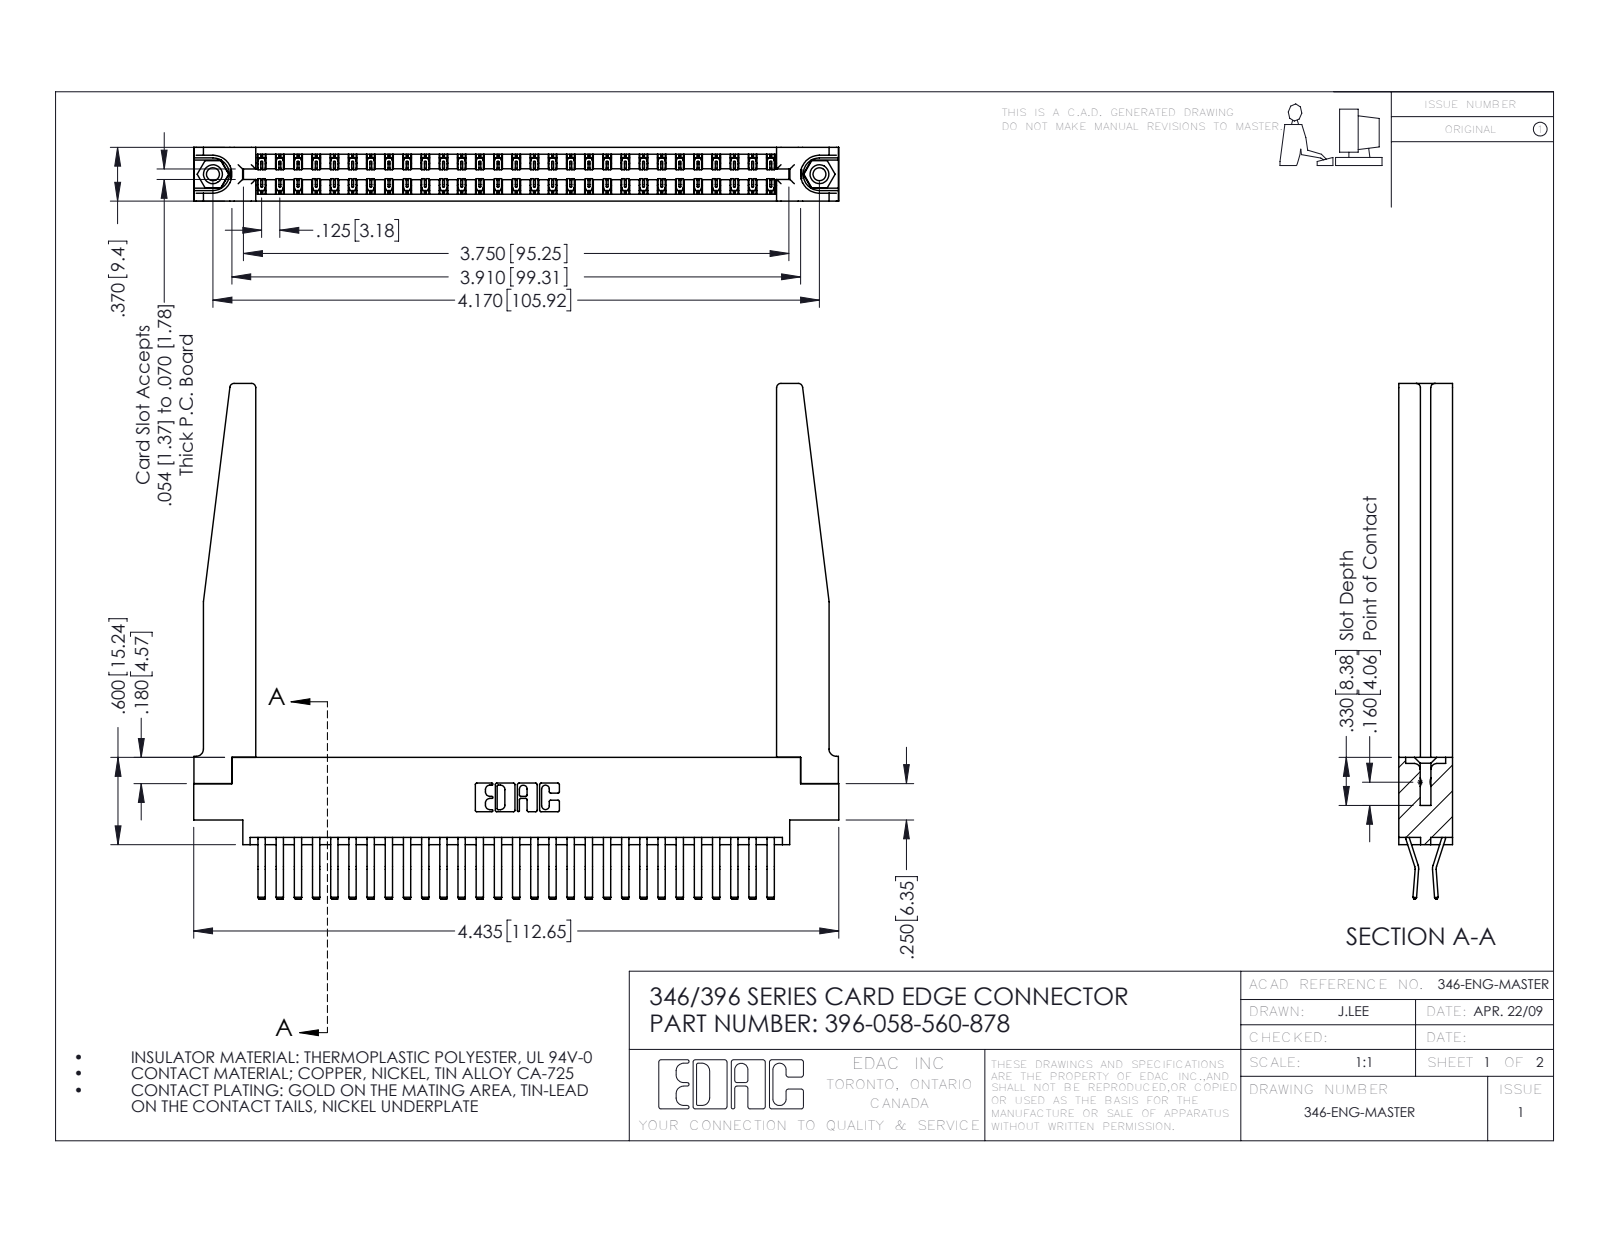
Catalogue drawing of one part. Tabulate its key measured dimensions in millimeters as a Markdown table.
| quantity | value |
| --- | --- |
| part name | 396-058-560-878; 345-292-001_560 Tail; 345-250-001_345-250-001-102; 346 Part_0.170 Offset - 0.156 Dia-TH (+1 more) |
| STEP written by | SolidWorks 2016 (CONFIG_CONTROL_DESIGN) |
| units | millimeters |
| bodies | 63 solids, 3492 faces (2252 planar, 1188 cylindrical, 52 other) |
| overall size | 112.6 × 90 × 9.4 |
| volume | 18 030 mm³ |
| surface area | 22 800 mm² |
| round holes (diameter × count) | 2.3 × 2, 3.2 × 2, 4 × 2, 1.6 × 1 |
| round bosses / shafts (diameter × count) | 3.9 × 2 |
| partial cylindrical surfaces (radius × count) | 0.2 × 87, 0.3 × 22, 0.8 × 8, 0.2 × 6, 0.8 × 6, 1.3 × 4, 0.7 × 3, 0.3 × 2 |
| main face-to-face distances | 9.4, 1.2, 8.2, 1.8, 3.8, 3.8, 0.6, 6.4, 7.6, 7 |
| hole center spacings | 6.2, 100.6, 105.9 |
